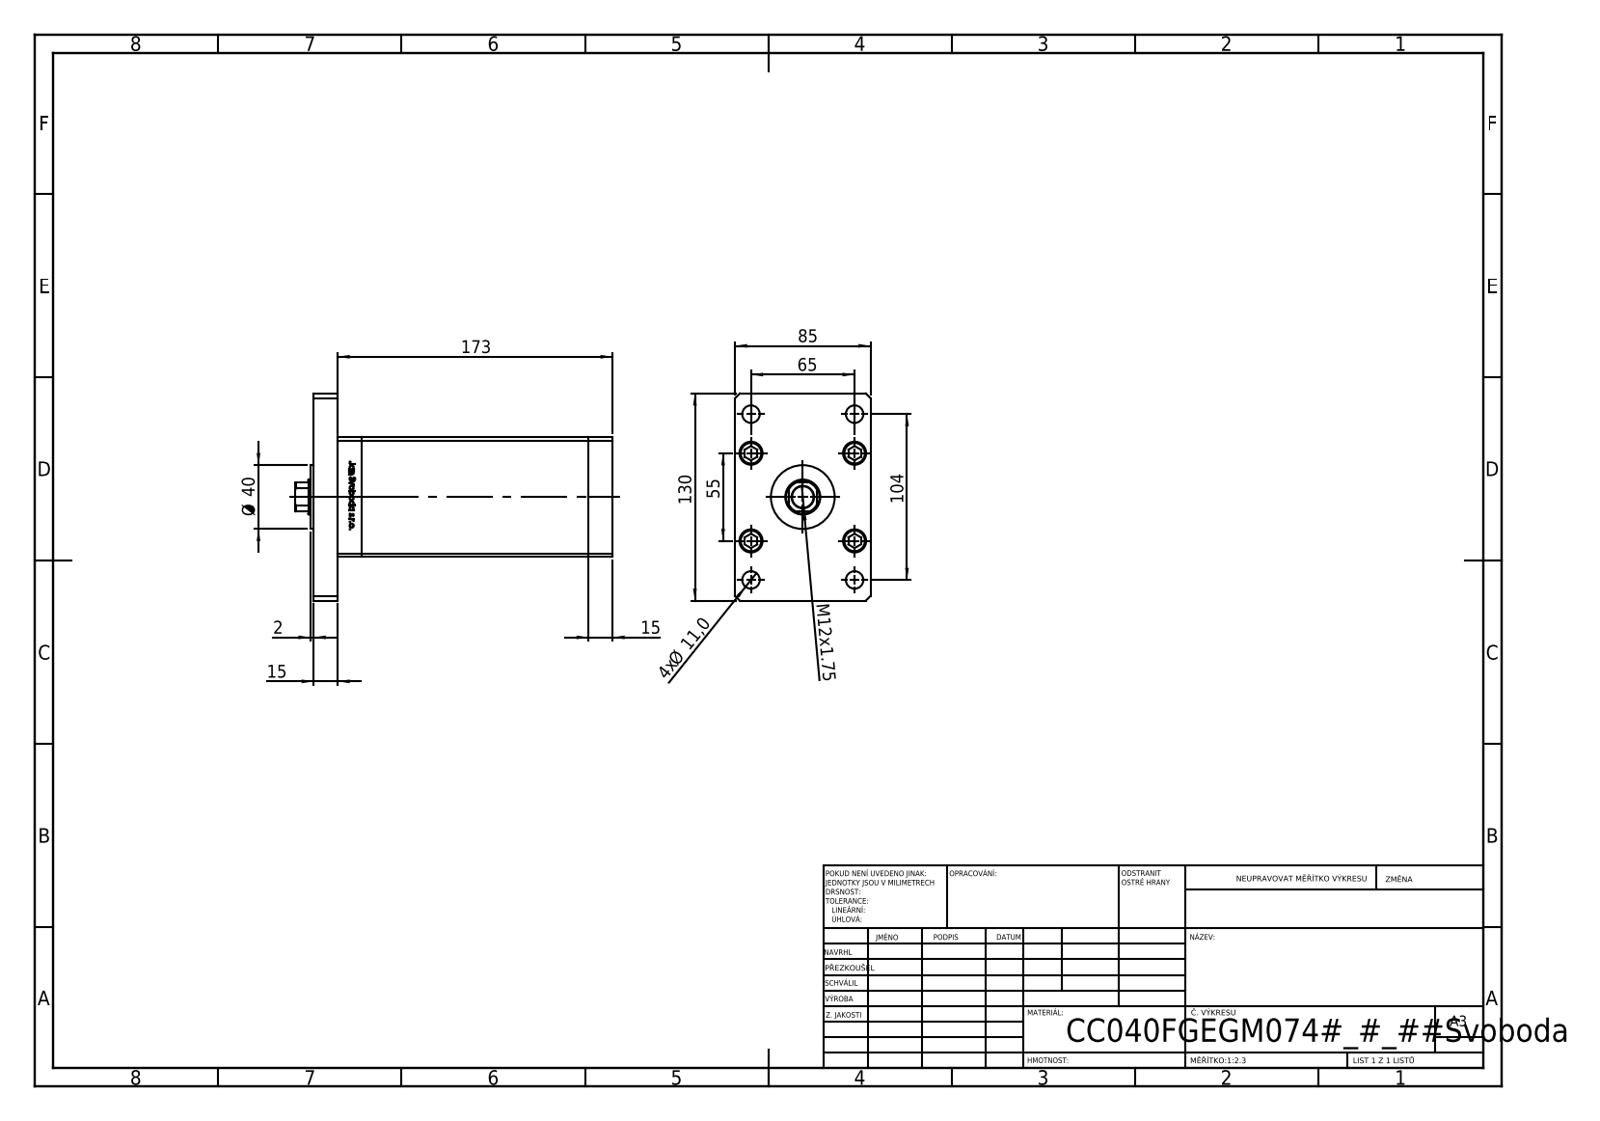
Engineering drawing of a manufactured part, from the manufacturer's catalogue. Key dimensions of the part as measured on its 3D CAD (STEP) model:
Part name (STEP PRODUCT): ALLEN BOLT; V220C_F_MIDDLE; V220C_F; V220C_FRONT_F (+2 more)
STEP written by: SolidWorks 2019 (CONFIG_CONTROL_DESIGN)
Units: millimetres
Bodies: 19 solids, 1310 faces (517 planar, 187 cylindrical, 606 other)
Overall size (bounding box): 199 × 130 × 85
Volume: 1 133 000 mm³ · Surface area: 195 682 mm²
Round holes (diameter × count): ⌀11 ×9, ⌀15.5 ×5, ⌀10 ×4, ⌀14.5 ×4, ⌀2 ×2, ⌀13.16 ×2, ⌀13.5 ×1, ⌀22 ×1, ⌀23.5 ×1
Round bosses / shafts (diameter × count): ⌀8 ×9, ⌀14.5 ×5, ⌀40 ×1
Partial cylindrical surfaces — rounded edges, fillets, slot ends (radius × count): R0.93 ×2, R10.5 ×1
Main face-to-face distances: 15, 85, 157.5, 172.5, 75, 30, 142.5, 187.5, 10.5, 27.5
Hole centre spacings: 28, 24.5, 42.57, 61.32, 65, 69.46, 79.5, 102.69
